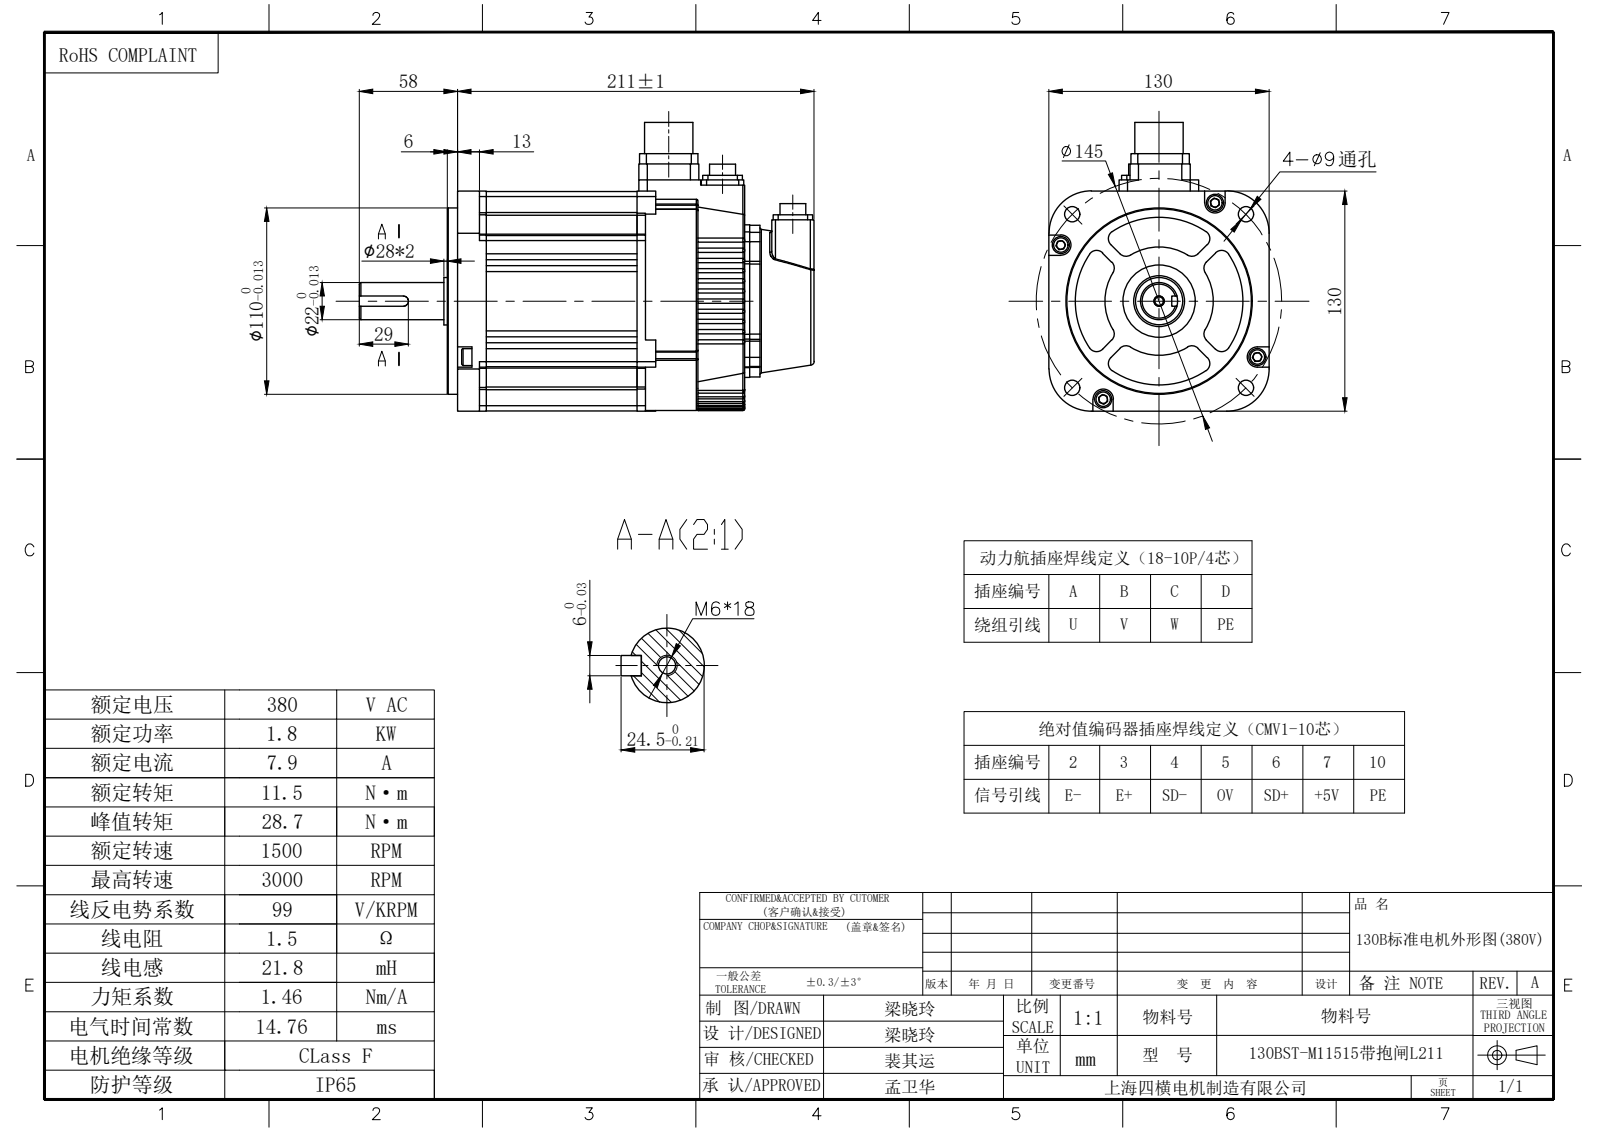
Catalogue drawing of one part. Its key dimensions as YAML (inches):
part_name: "130BST机身89; 130BST后端盖02; hexagon socket head cap screws gb_ M6; 130BST-M11515带抱闸L211 (+2 more)"
step_written_by: "SolidWorks 2020 (AUTOMOTIVE_DESIGN)"
units: inches
bodies: {solids: 8, faces: 1030, planar: 411, cylindrical: 412, other: 207}
overall_size: [10.571, 6.713, 5.118]
volume: 161.7
surface_area: 370.2
round_holes:
  - {diameter: 0.118, count: 14}
  - {diameter: 0.26, count: 8}
  - {diameter: 0.197, count: 5}
  - {diameter: 0.354, count: 4}
  - {diameter: 0.453, count: 2}
  - {diameter: 0.945, count: 1}
  - {diameter: 1.677, count: 1}
round_bosses_or_shafts:
  - {diameter: 0.394, count: 4}
  - {diameter: 0.236, count: 4}
  - {diameter: 0.098, count: 4}
  - {diameter: 0.602, count: 2}
  - {diameter: 0.079, count: 2}
  - {diameter: 5.079, count: 1}
  - {diameter: 4.331, count: 1}
  - {diameter: 1.181, count: 1}
partial_cylinders:
  - {radius: 0.039, count: 61}
  - {radius: 0.118, count: 25}
  - {radius: 0.197, count: 22}
  - {radius: 0.059, count: 16}
  - {radius: 0.128, count: 16}
  - {radius: 0.079, count: 8}
  - {radius: 0.138, count: 8}
  - {radius: 0.089, count: 4}
face_to_face_distances: [3.504, 6.004, 2.5, 4.173, 0.669, 6.673, 5.098, 1.024, 4.075, 4.085]
hole_center_spacings: [0.709, 0.053, 0.473, 0.501, 0.669, 1.063, 2.627, 2.667]
